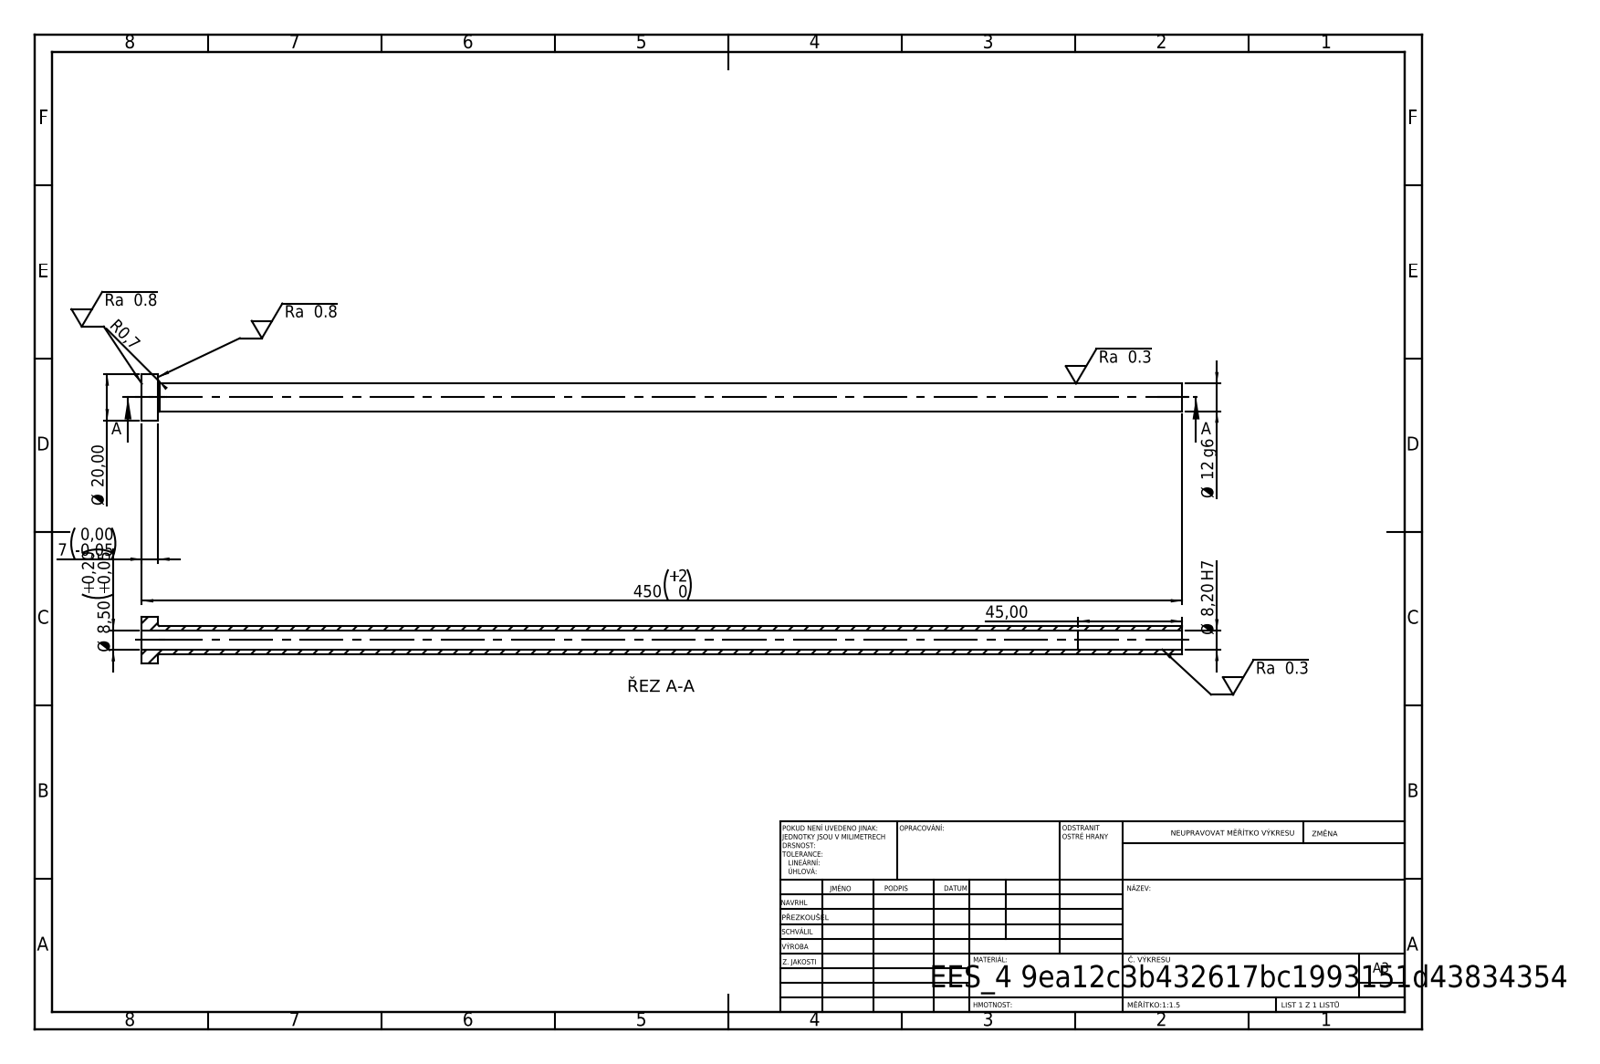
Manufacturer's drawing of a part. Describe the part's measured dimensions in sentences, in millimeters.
Its 3-D file was written by "SolidWorks 2019 (CONFIG_CONTROL_DESIGN)". It is 1 solid with 14 faces: 4 planar, 8 cylindrical and 2 other. Overall it measures 450 by 20 by 20 millimeters. Its volume is 26 947 cubic millimeters and its surface area 29 626 square millimeters. Round holes: 1 of diameter 8.2, 1 of diameter 8.5. Round bosses or shafts: 1 of diameter 20, 1 of diameter 12. The main face-to-face distances are 7, 450, 443, 405, 398, 45.
